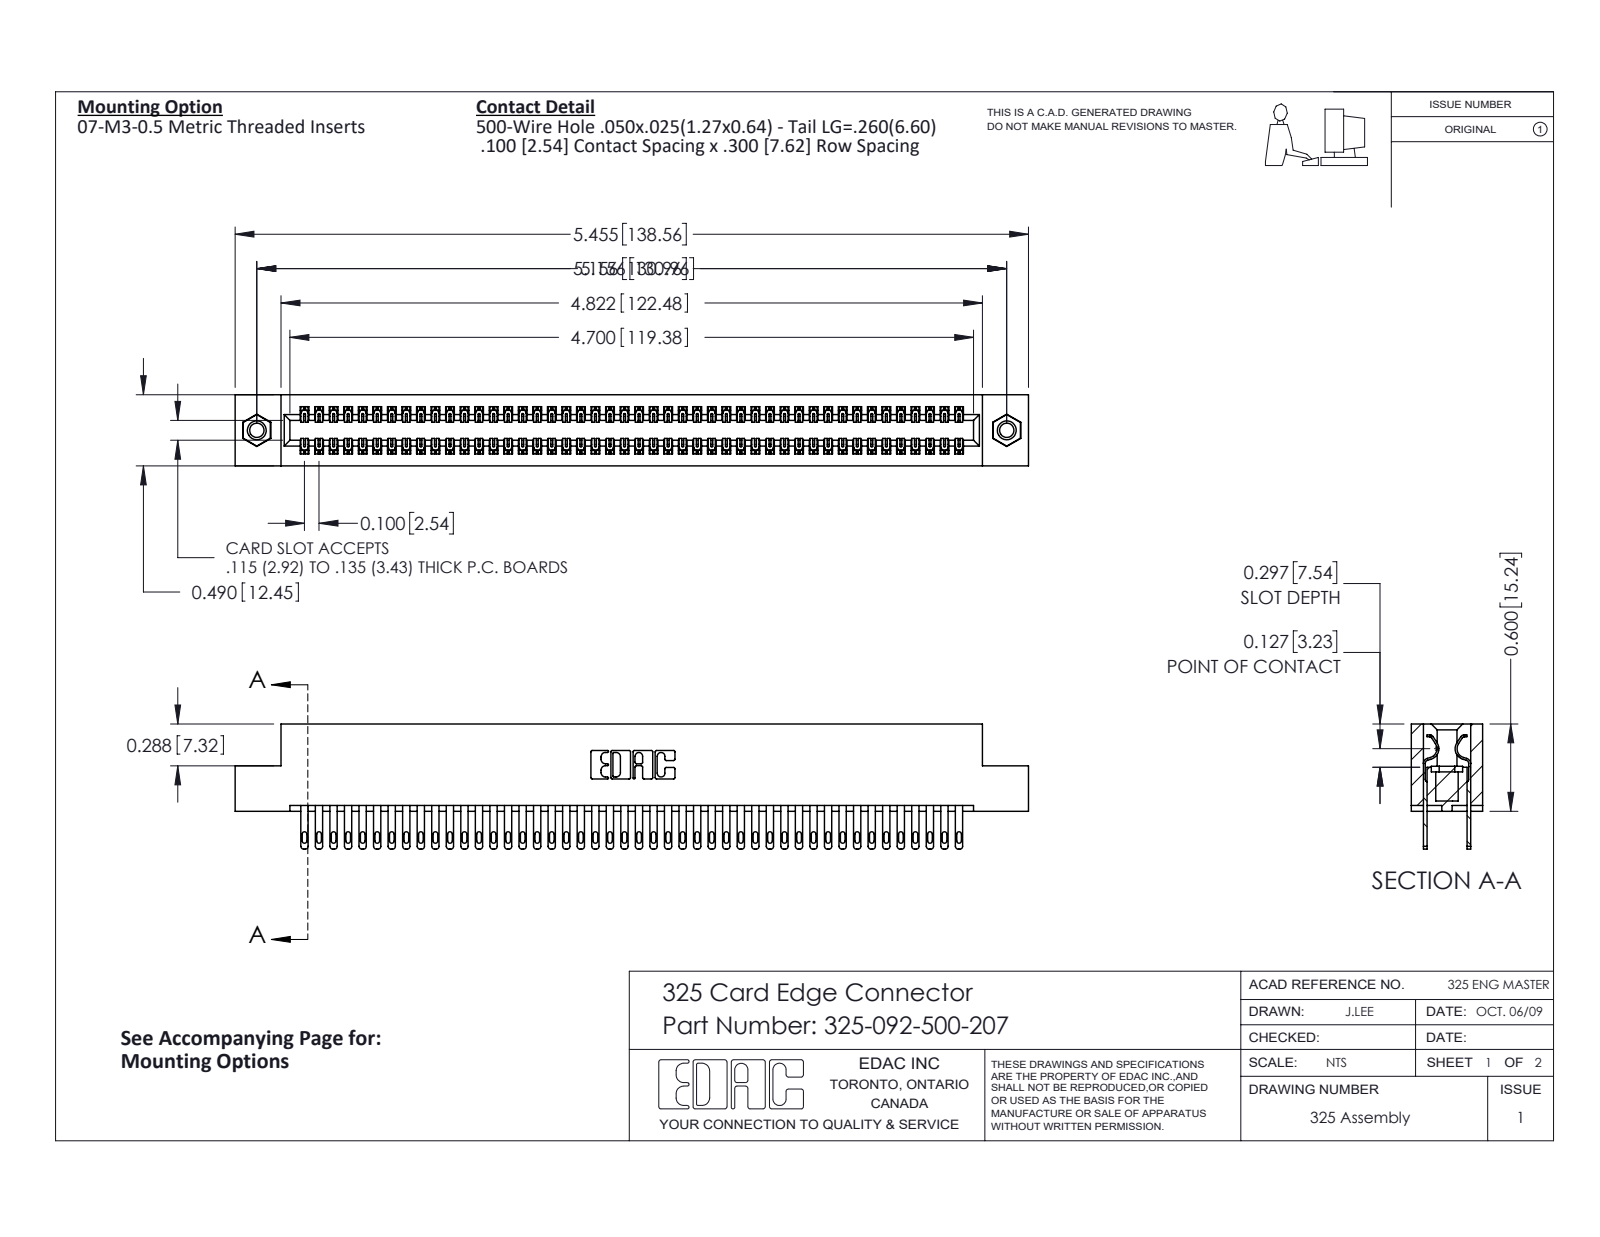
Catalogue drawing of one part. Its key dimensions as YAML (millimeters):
part_name: "325-292-001_325-293-100; 325-092-500-207; 345-250-001_345-250-005-103; 325 Part_TI"
step_written_by: "SolidWorks 2016 (CONFIG_CONTROL_DESIGN)"
units: millimeters
bodies: {solids: 95, faces: 4590, planar: 2862, cylindrical: 1712, other: 16}
overall_size: [138.6, 21.8, 12.4]
volume: 18190
surface_area: 23100
round_holes:
  - {diameter: 2.5, count: 2}
  - {diameter: 3.2, count: 2}
  - {diameter: 4.1, count: 2}
round_bosses_or_shafts:
  - {diameter: 3.9, count: 2}
partial_cylinders:
  - {radius: 0.2, count: 138}
  - {radius: 0.4, count: 92}
  - {radius: 0.5, count: 92}
  - {radius: 0.3, count: 22}
  - {radius: 0.2, count: 6}
  - {radius: 0.8, count: 6}
  - {radius: 0.7, count: 3}
  - {radius: 0.4, count: 2}
face_to_face_distances: [2.1, 10.3, 7.6, 2.7, 9.7, 0.6, 12.4, 8.3, 7, 14.2]
hole_center_spacings: [131]
